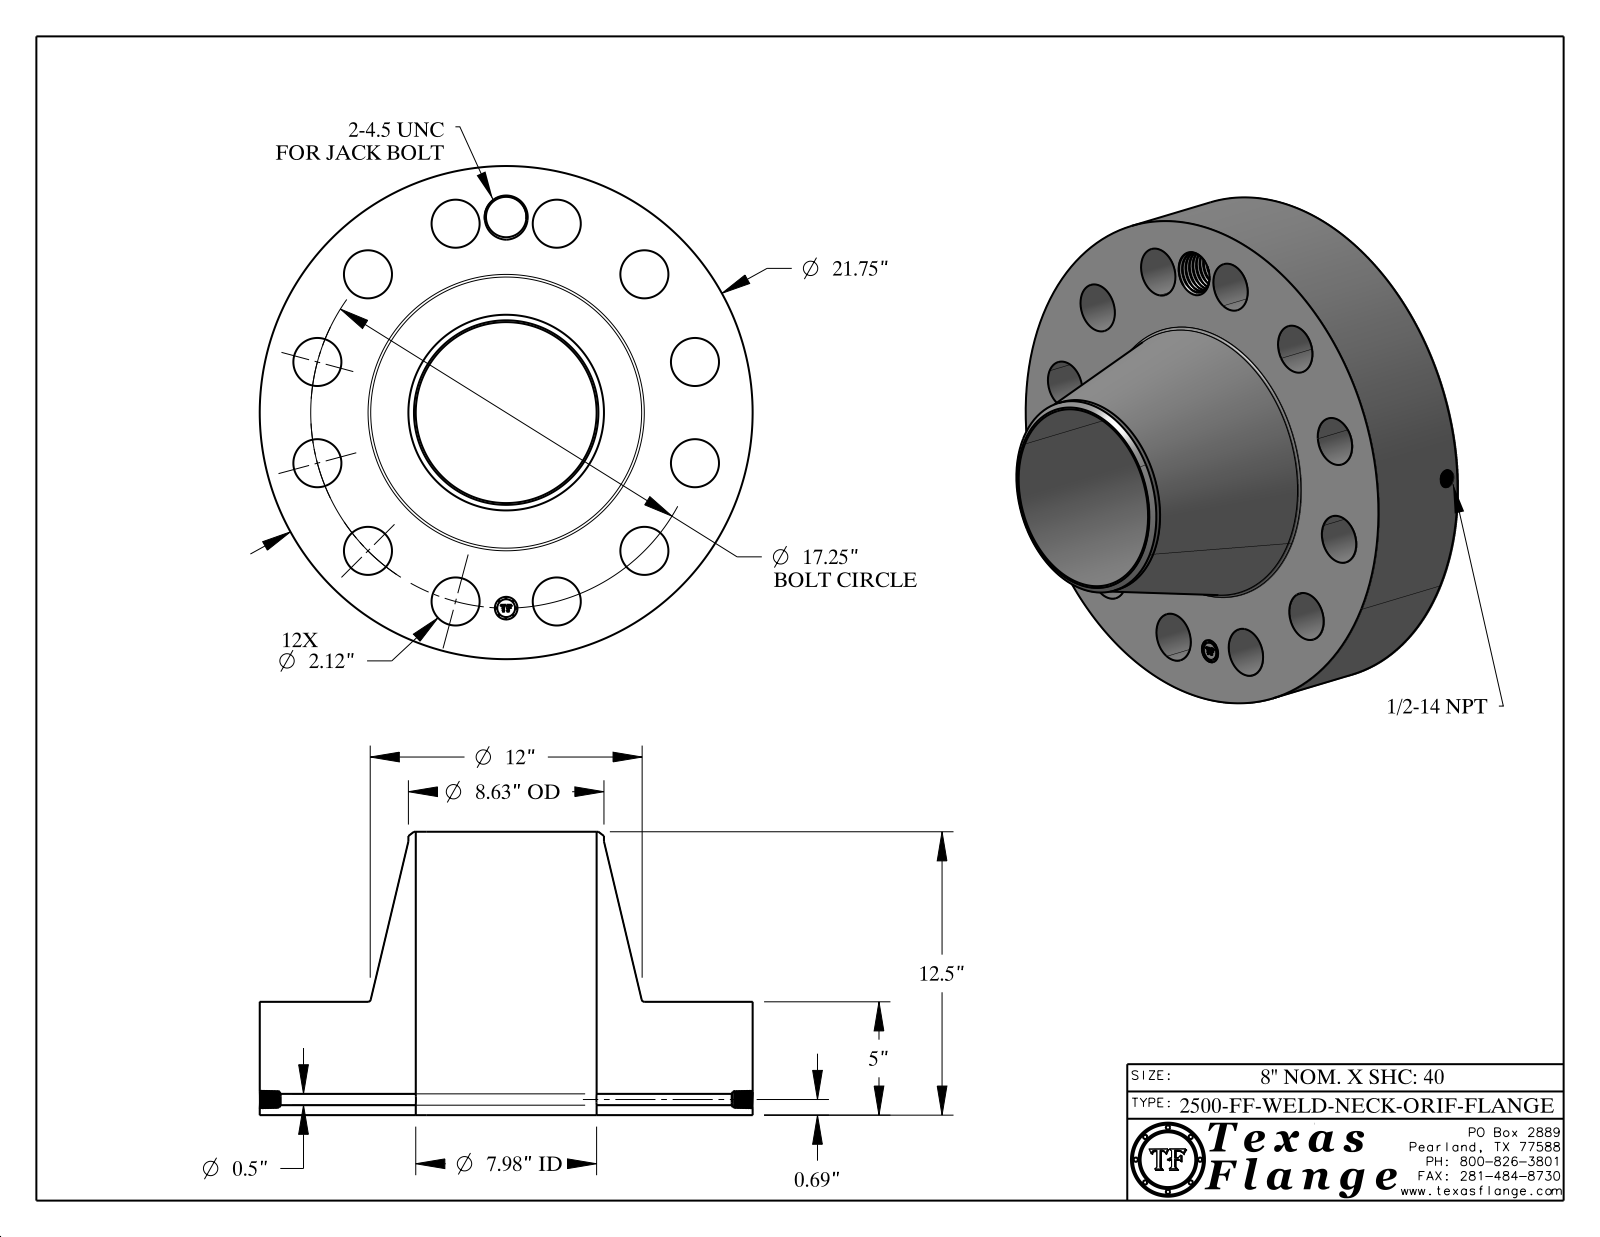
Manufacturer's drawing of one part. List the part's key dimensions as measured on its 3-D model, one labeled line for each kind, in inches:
Part name (STEP PRODUCT): 2500-FF-WELD-NECK
STEP written by: CATIA V5 STEP AP214 (AUTOMOTIVE_DESIGN)
Units: inches
Bodies: 1 solid, 820 faces (368 planar, 115 cylindrical, 337 other)
Overall size (bounding box): 21.75 × 21.75 × 12.5
Volume: 1 624 in³ · Surface area: 1 862 in²
Round holes (diameter × count): ⌀2.12 ×12, ⌀0.5 ×1, ⌀0.672 ×1, ⌀1 ×1, ⌀1.781 ×1, ⌀7.981 ×1
Round bosses / shafts (diameter × count): ⌀0.061 ×8, ⌀21.75 ×1, ⌀8.63 ×1, ⌀0.788 ×1
Main face-to-face distances: 5, 12.5, 7.5, 0.015, 4.985, 7.515, 0.298, 0.292, 0.054, 0.248
Hole centre spacings: 8.625, 4.465, 12.198, 14.939, 16.662, 8.625, 17.25, 2.252
